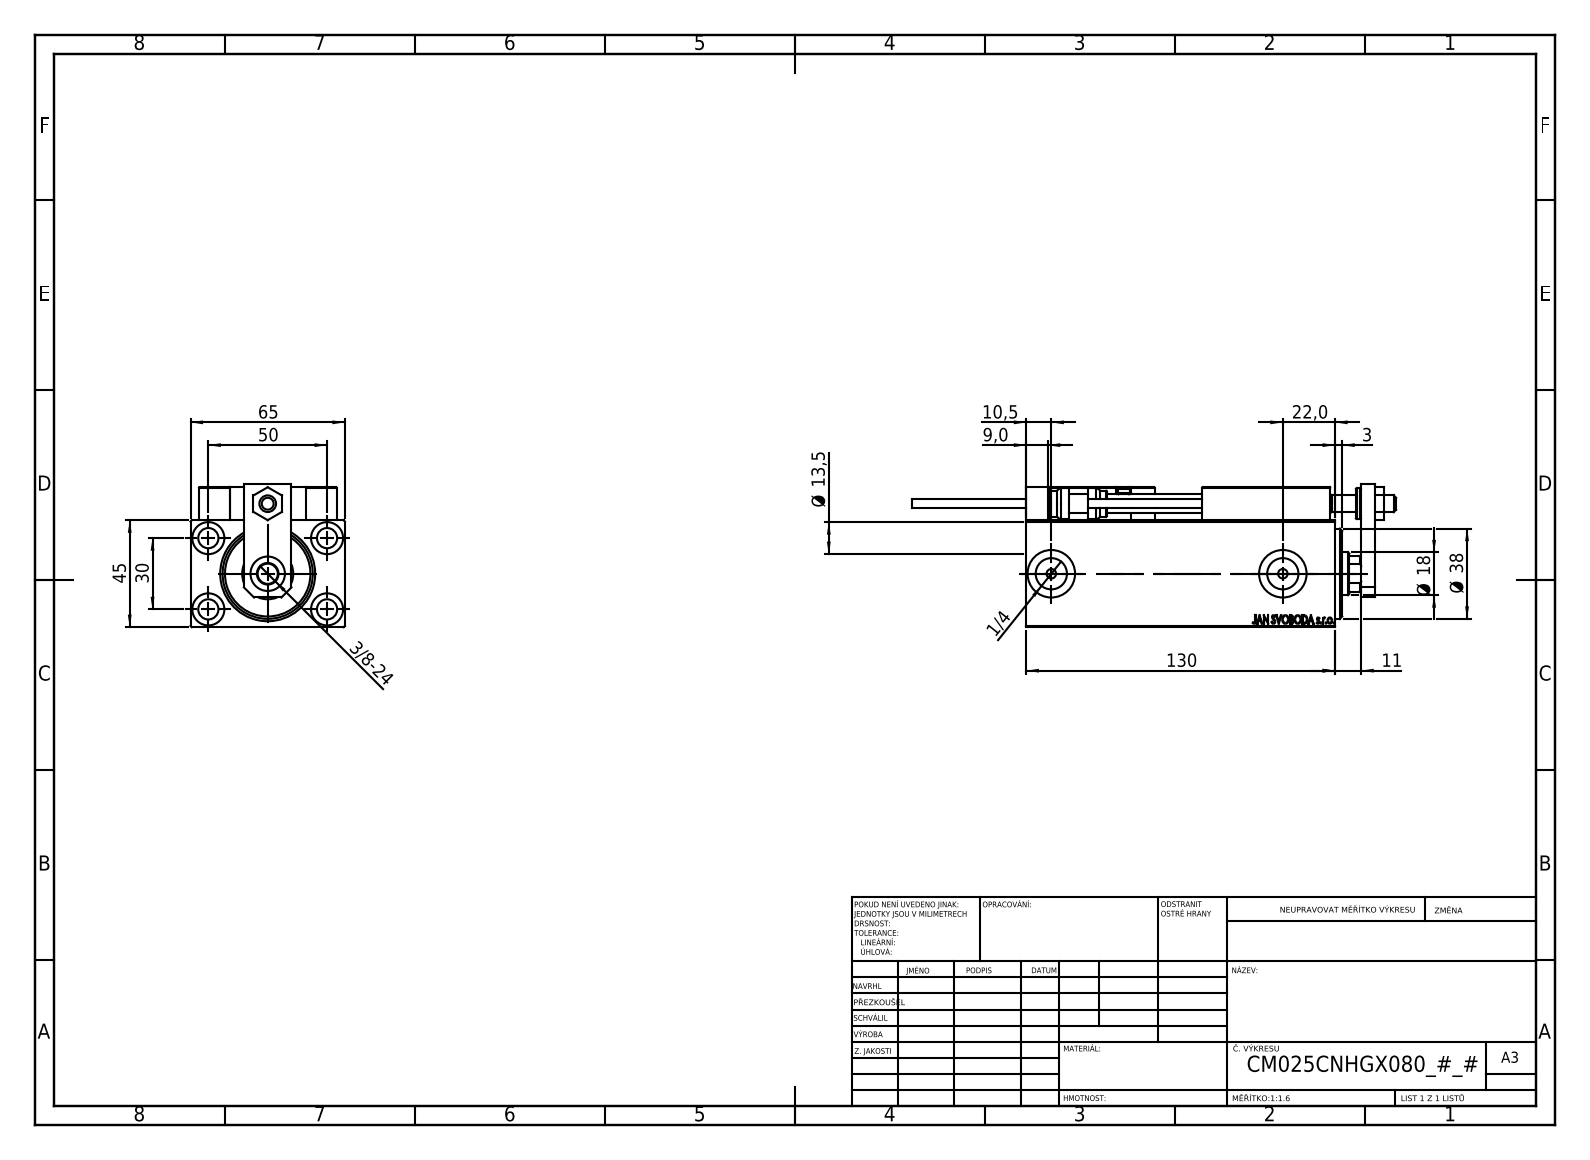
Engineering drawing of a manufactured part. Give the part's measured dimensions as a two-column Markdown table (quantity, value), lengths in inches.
| quantity | value |
| --- | --- |
| part name | ALLEN BOLT D5; SWITCH_X_FRONT_BACK; NUT_D12; KONCOVKA (+8 more) |
| STEP written by | SolidWorks 2019 (CONFIG_CONTROL_DESIGN) |
| units | inches |
| bodies | 23 solids, 1282 faces (560 planar, 188 cylindrical, 534 other) |
| overall size | 8.02 × 2.559 × 2.382 |
| volume | 22.81 in³ |
| surface area | 152.4 in² |
| round holes (diameter × count) | 0.157 × 6, 0.315 × 5, 0.335 × 5, 0.126 × 4, 0.531 × 4, 0.197 × 2, 0.518 × 2, 0.787 × 2, 0.276 × 1, 0.571 × 1, 0.709 × 1, 0.846 × 1 |
| round bosses / shafts (diameter × count) | 0.197 × 2, 0.15 × 2, 0.512 × 1, 0.433 × 1 |
| partial cylindrical surfaces (radius × count) | 0.012 × 30, 0.118 × 2, 0.335 × 1 |
| main face-to-face distances | 1.772, 2.559, 0.551, 0.236, 2.323, 0.118, 0.512, 0.138, 0.276, 0.787 |
| hole center spacings | 1.148, 0.448, 0.787, 1.138, 1.165, 1.169, 1.181, 1.42 |
